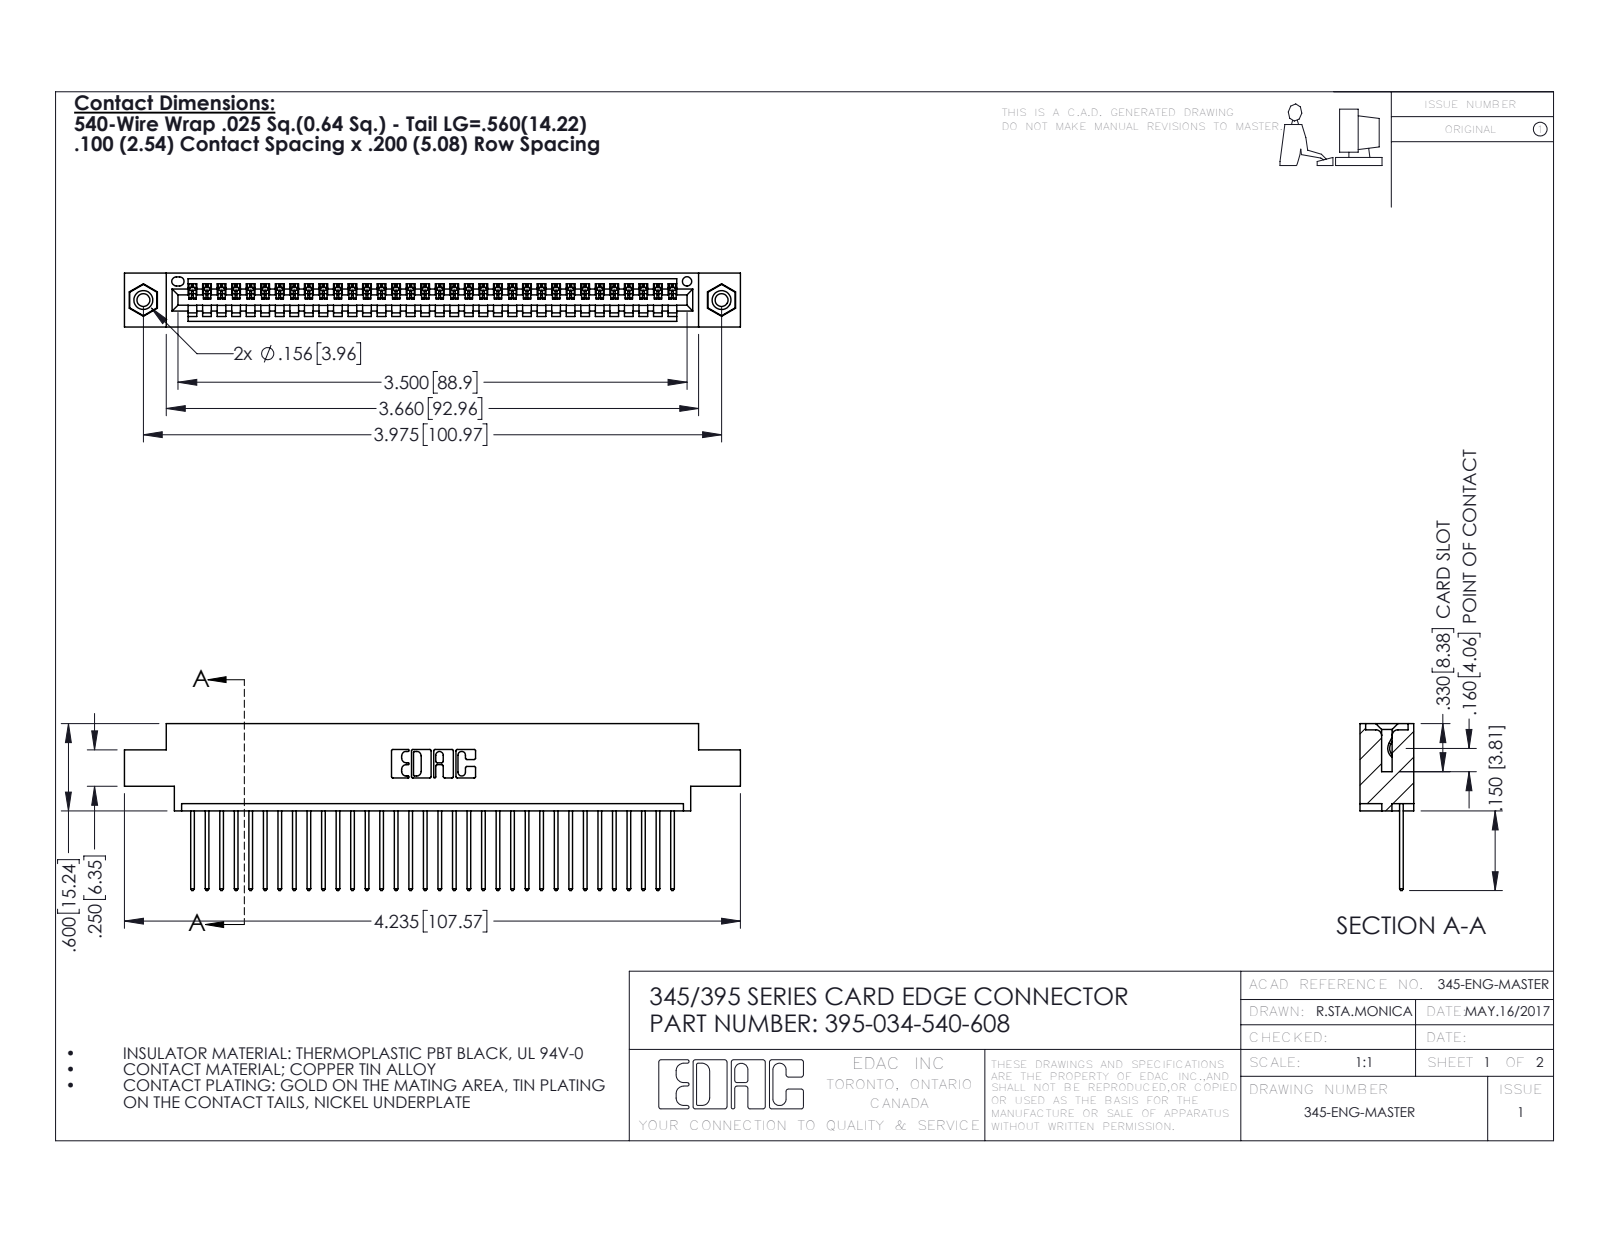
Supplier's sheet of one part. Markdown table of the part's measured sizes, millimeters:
| quantity | value |
| --- | --- |
| part name | 345-292-001_345-293-140; 345 Part_0.170 Offset - 0.156 Dia-TI; 395-034-540-608; 345-250-001_345-250-003-102 |
| STEP written by | SolidWorks 2016 (CONFIG_CONTROL_DESIGN) |
| units | millimeters |
| bodies | 37 solids, 2162 faces (1476 planar, 670 cylindrical, 16 other) |
| overall size | 107.6 × 29.1 × 9.4 |
| volume | 10 100 mm³ |
| surface area | 13 760 mm² |
| round holes (diameter × count) | 2.3 × 2, 3.2 × 2, 4 × 2, 1.6 × 1 |
| round bosses / shafts (diameter × count) | 3.9 × 2 |
| partial cylindrical surfaces (radius × count) | 0.2 × 68, 0.3 × 68, 0.3 × 22, 0.2 × 6, 0.8 × 6, 0.7 × 3, 0.8 × 2, 1 × 2 |
| main face-to-face distances | 1.8, 7.6, 9.4, 2.5, 6.9, 0.6, 5.1, 5.7, 4.4, 3.8 |
| hole center spacings | 6.9, 95, 101 |
